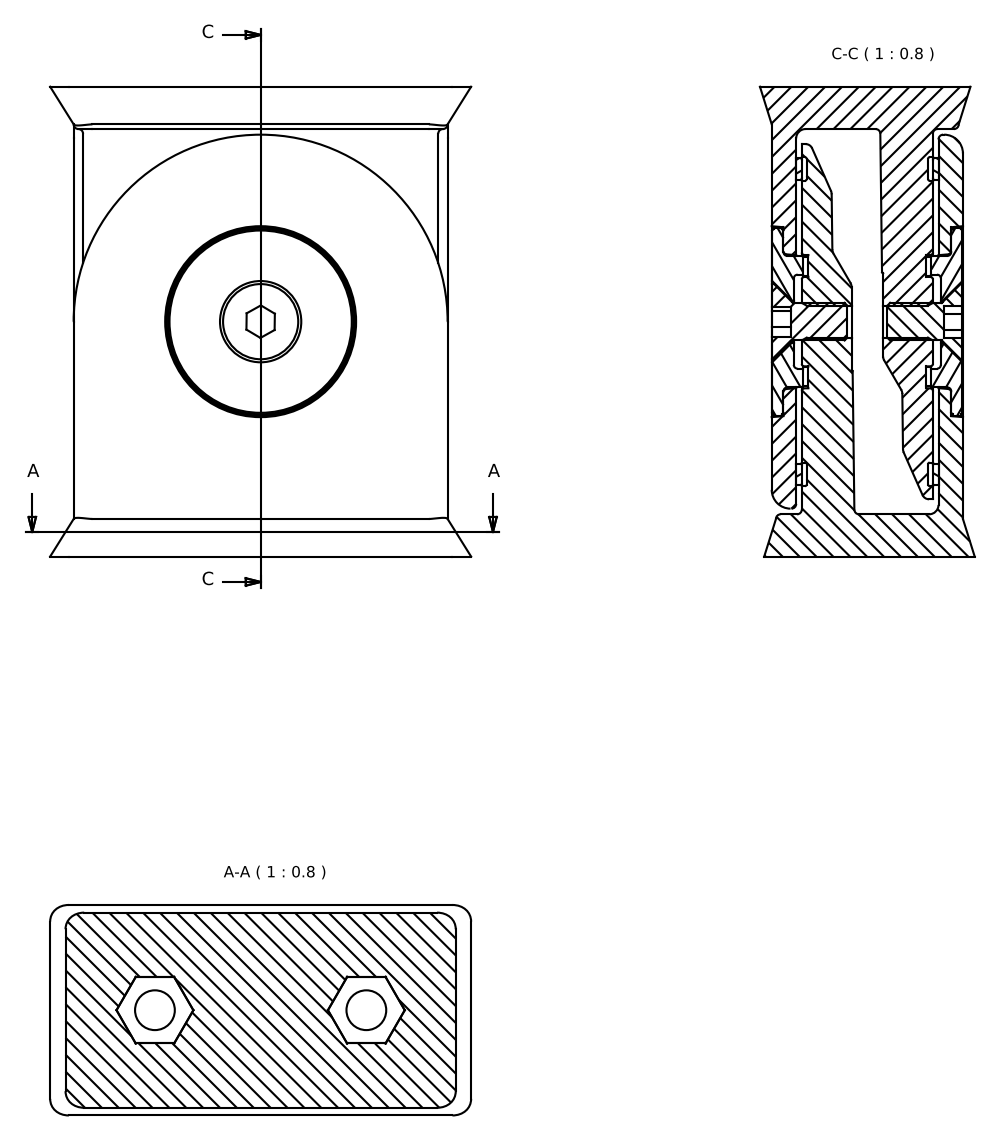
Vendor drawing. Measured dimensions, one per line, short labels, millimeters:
name: CGIPR0000113; 440000009825; 440000009822; 440000009823 (+1 more)
written by: Autodesk Inventor 2022 (AUTOMOTIVE_DESIGN)
unit: mm
bodies: 8 solids, 438 faces (178 planar, 118 cylindrical, 142 other)
size: 100 × 89.6 × 45.7
volume: 188 004 mm³; area: 78 925 mm²
holes: 1× ⌀6.8, 1× ⌀9, 1× ⌀20, 1× ⌀60.4, 1× ⌀70
bosses: 2× ⌀2, 1× ⌀79.6, 1× ⌀75.6, 1× ⌀69.6, 1× ⌀60, 1× ⌀40, 1× ⌀28, 1× ⌀16
rounds: 36× R1, 16× R2, 12× R4, 4× R1.5, 2× R2.5
face distances: 1.2, 29.1, 5.2, 6.4, 34.3, 35.5, 30.3, 27.9, 100, 40.7
